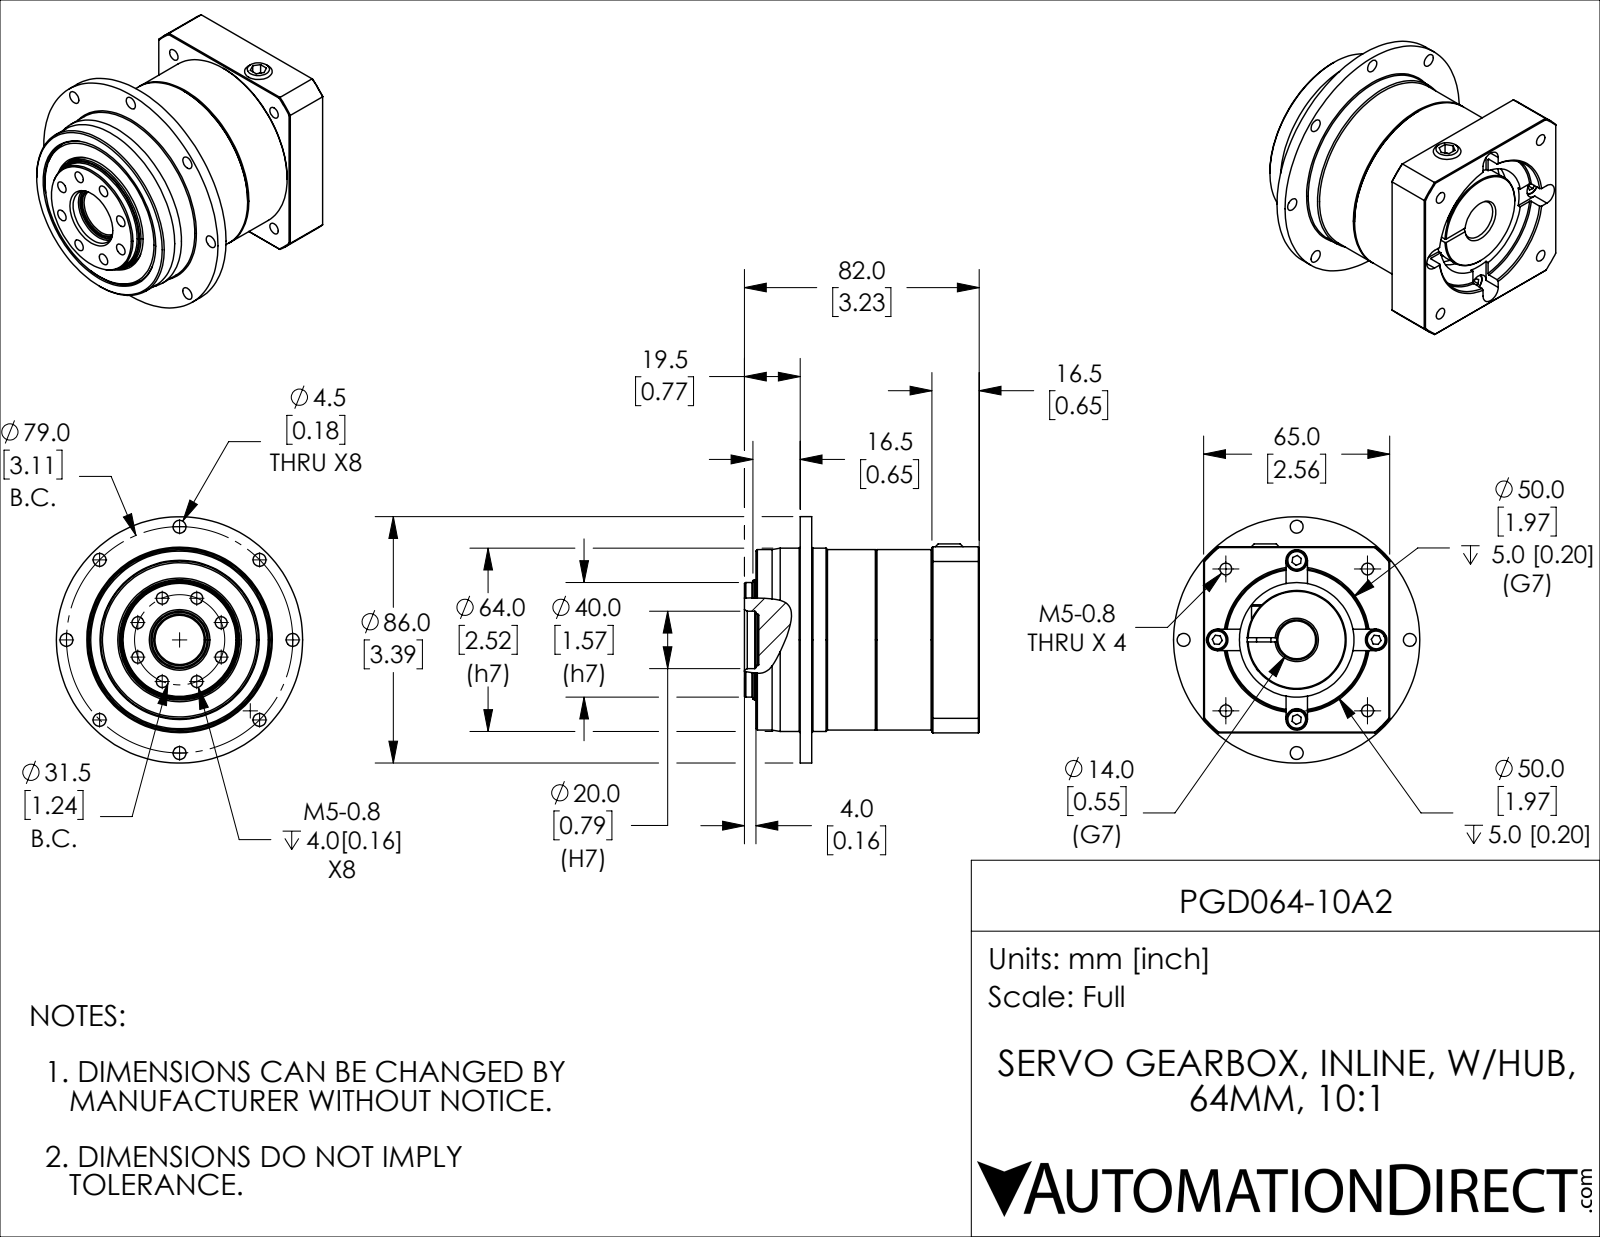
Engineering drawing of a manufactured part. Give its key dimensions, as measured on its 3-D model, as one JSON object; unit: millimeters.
{"part_name": "PGD064-10A2", "step_written_by": "SolidWorks 2015 (AUTOMOTIVE_DESIGN)", "units": "millimeters", "bodies": {"solids": 10, "faces": 372, "planar": 127, "cylindrical": 150, "other": 95}, "overall_size": [86, 86, 82], "volume_mm3": 251466, "surface_area_mm2": 42273, "round_holes": [[4.13, 12], [4.5, 9], [7.5, 4], [5, 2], [3.24, 1], [4, 1], [8, 1], [14, 1], [20, 1], [40, 1], [50, 1]], "round_bosses_or_shafts": [[86, 1], [64, 1], [63, 1], [42, 1], [29, 1], [7, 1], [4, 1]], "partial_cylinders_radius": [[42.5, 1]], "face_to_face_distances": [4, 62.5, 65, 58.5, 16.5, 19, 81.5, 23, 1, 19.5], "hole_center_spacings": [36.5, 54.39, 15.75, 14.51, 21.32, 22.27, 24.93, 25.66]}
